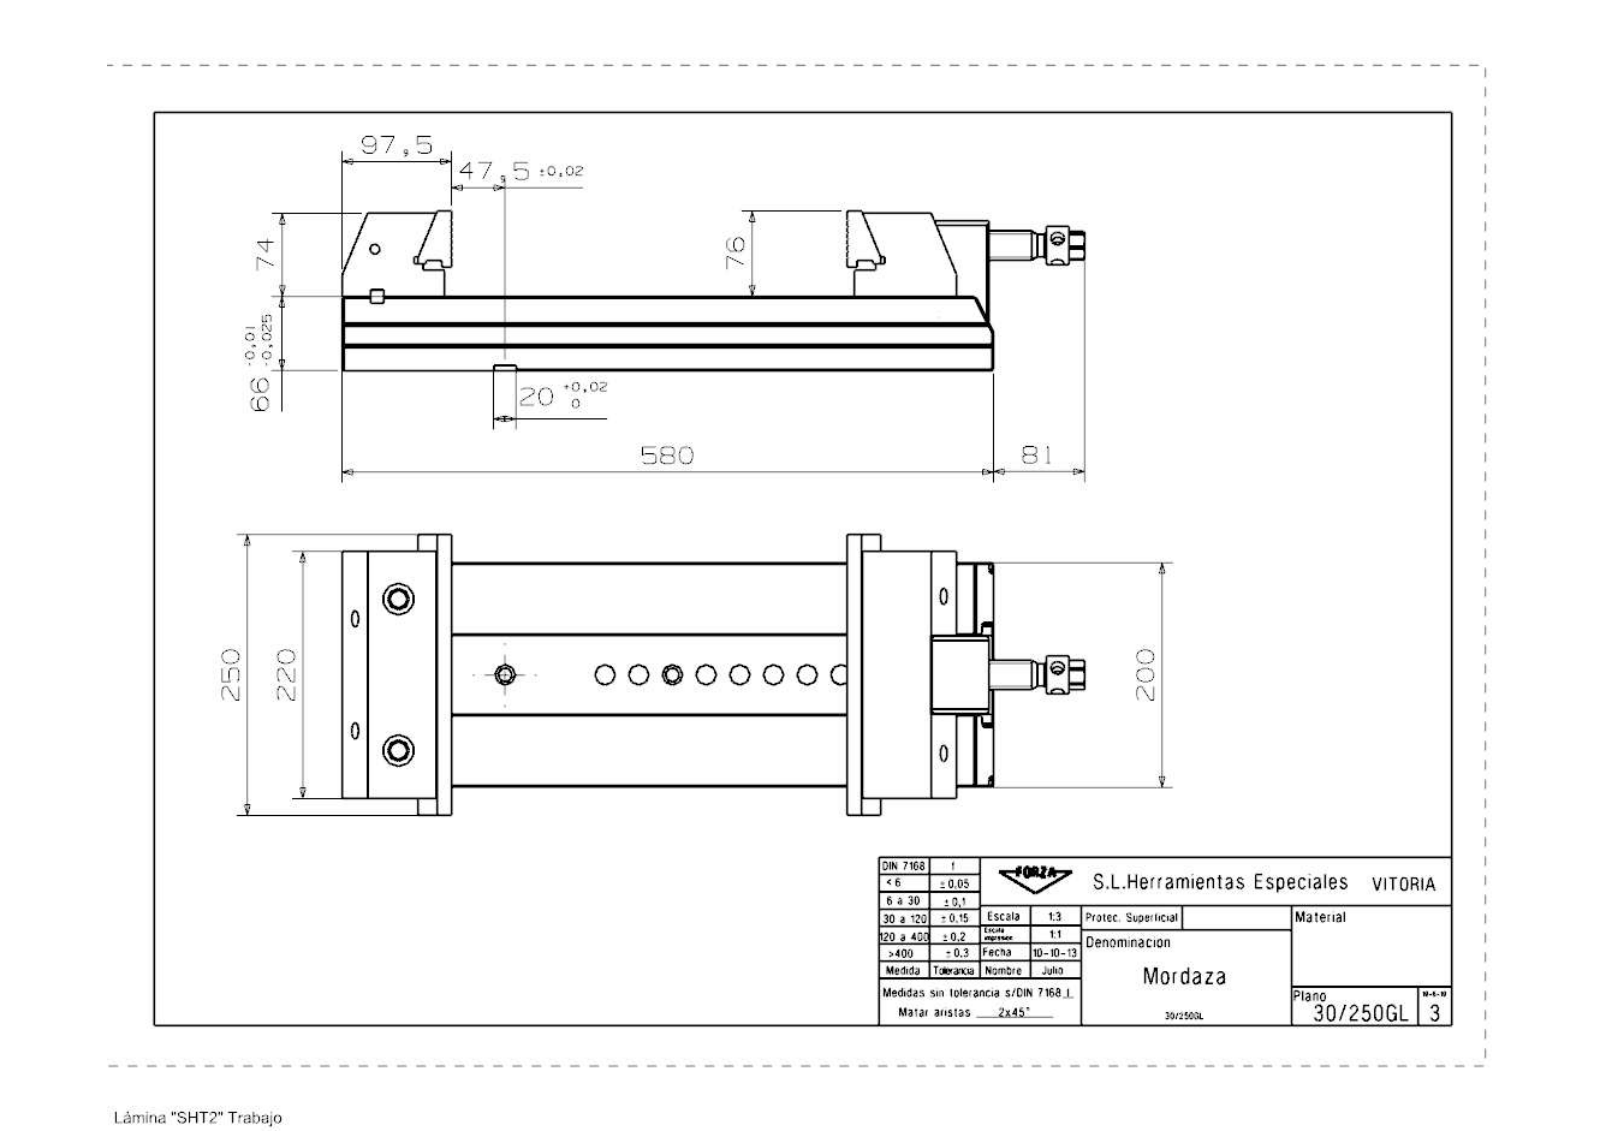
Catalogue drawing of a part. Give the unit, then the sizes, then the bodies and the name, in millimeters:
Units: millimetres
Overall size (bounding box): 661 × 250 × 142
Round holes (diameter × count): ⌀5.19 ×6, ⌀19 ×5, ⌀9.5 ×4, ⌀15 ×4, ⌀18 ×4, ⌀8.78 ×3, ⌀10.58 ×3, ⌀12.38 ×3, ⌀13 ×3, ⌀6.5 ×2, ⌀6.99 ×2, ⌀8.5 ×2
Round bosses / shafts (diameter × count): ⌀34 ×1, ⌀33.8 ×1, ⌀26 ×1, ⌀20 ×1, ⌀16.5 ×1
Partial cylindrical surfaces — rounded edges, fillets, slot ends (radius × count): R10 ×8, R6.5 ×2, R9 ×1, R10.5 ×1, R12.5 ×1, R13.25 ×1
Main face-to-face distances: 66, 33.7, 32.3, 1.5, 64.5, 10, 32.2, 65, 145, 140
Hole centre spacings: 20, 21, 24.74, 27.31, 29.06, 30, 35.38, 46.32
Volume: 8 907 000 mm³ · Surface area: 801 238 mm²
Bodies: 12 solids, 632 faces (470 planar, 103 cylindrical, 59 other)
Part name (STEP PRODUCT): 3025090 Taco completo Atras; 30_250GL_Mordaza
STEP written by: SIEMENS PLM Software NX 11.0 (AUTOMOTIVE_DESIGN)
